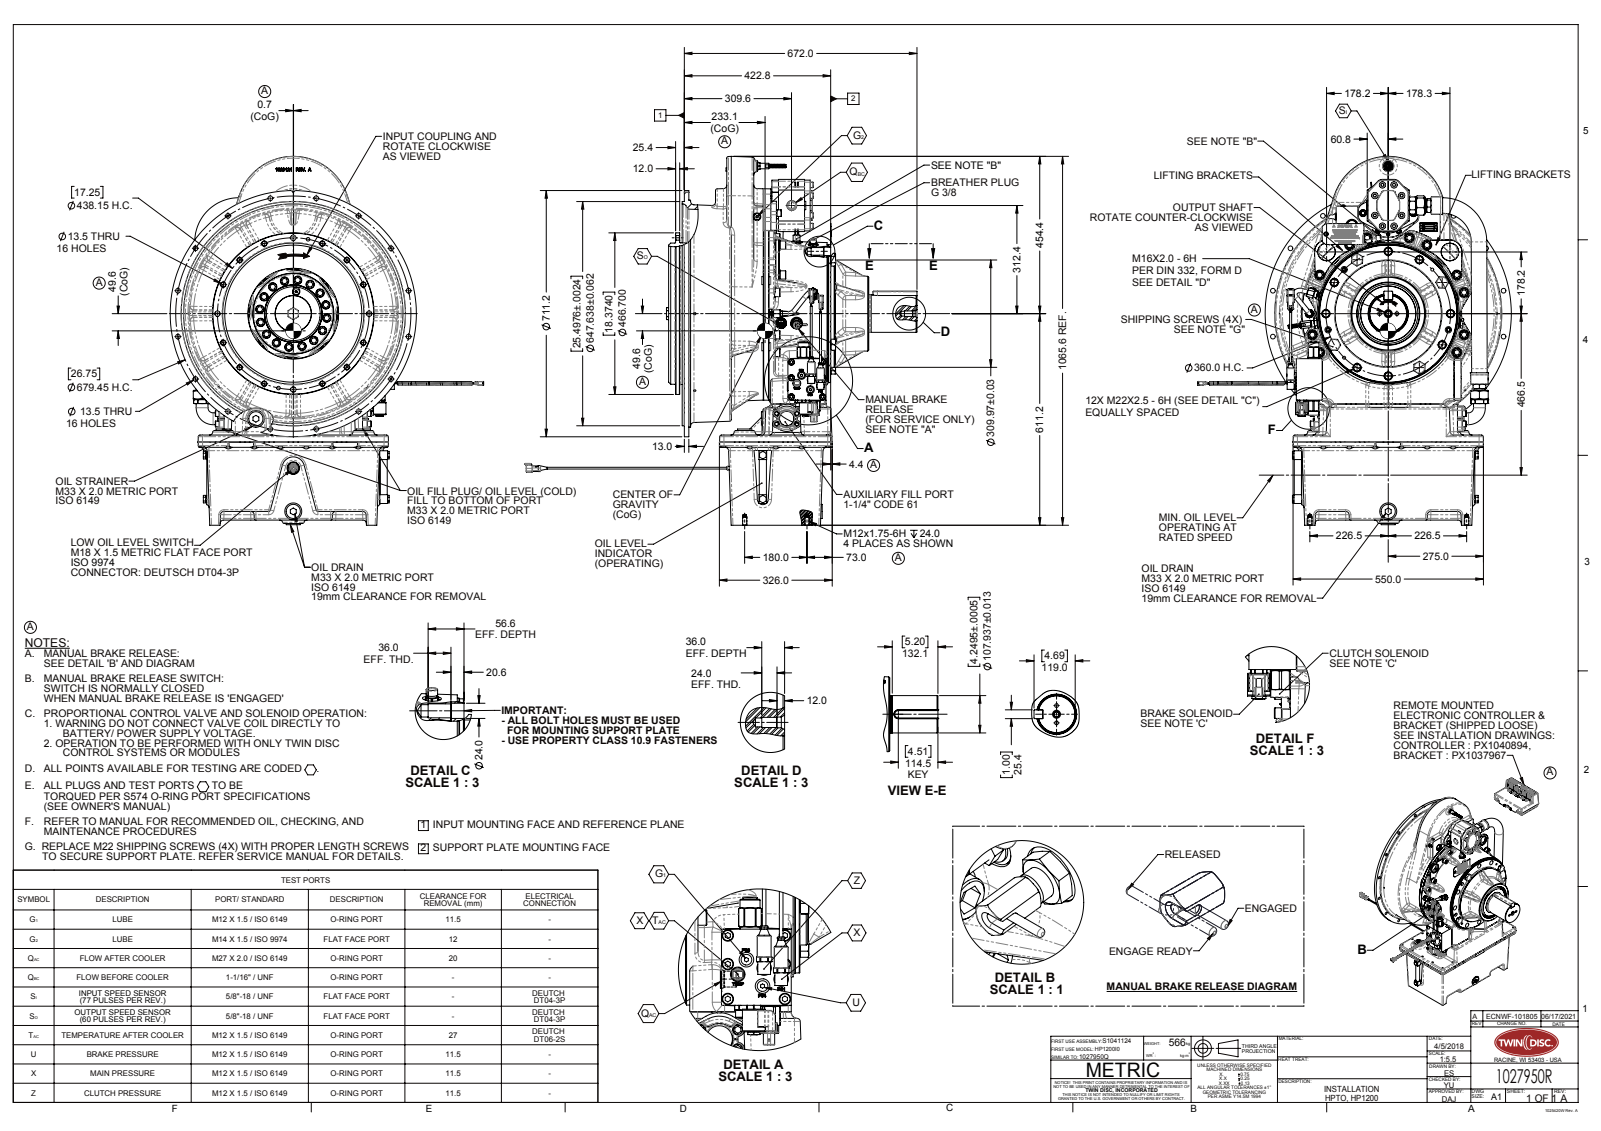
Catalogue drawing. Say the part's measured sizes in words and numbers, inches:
The part is named "1027950R". Its 3-D file was written by "SolidWorks 2019 (AUTOMOTIVE_DESIGN)". It is 0 solids with 4978 faces: 1865 planar, 1511 cylindrical and 1602 other. Overall it measures 46.104 by 44.573 by 35.657 inches. Round holes: 32 of diameter 0.531, 26 of diameter 0.945, 23 of diameter 0.118, 22 of diameter 0.433, 20 of diameter 0.335, 9 of diameter 0.709, 7 of diameter 1.063, 5 of diameter 1.181, 4 of diameter 0.283, 4 of diameter 0.472, 4 of diameter 1.339, 3 of diameter 0.201. Round bosses or shafts: 29 of diameter 0.945, 26 of diameter 0.063, 10 of diameter 0.63, 6 of diameter 0.394, 4 of diameter 1.606, 4 of diameter 1.102, 4 of diameter 0.75, 4 of diameter 0.656. Partial cylindrical surfaces (rounded edges, fillets, slot ends): 124 of radius 0.197, 105 of radius 0.394, 43 of radius 0.039, 24 of radius 0.118, 16 of radius 0.157, 15 of radius 0.05, 13 of radius 0.024, 10 of radius 0.025. The main face-to-face distances are 0.024, 0.614, 4.823, 0.591, 0.512, 4.154, 4.177, 4.768, 0.811, 11.377. The hole center spacings are 2.953, 14.764, 5.906, 12.174, 11.811, 13.205, 8.625, 8.858.
